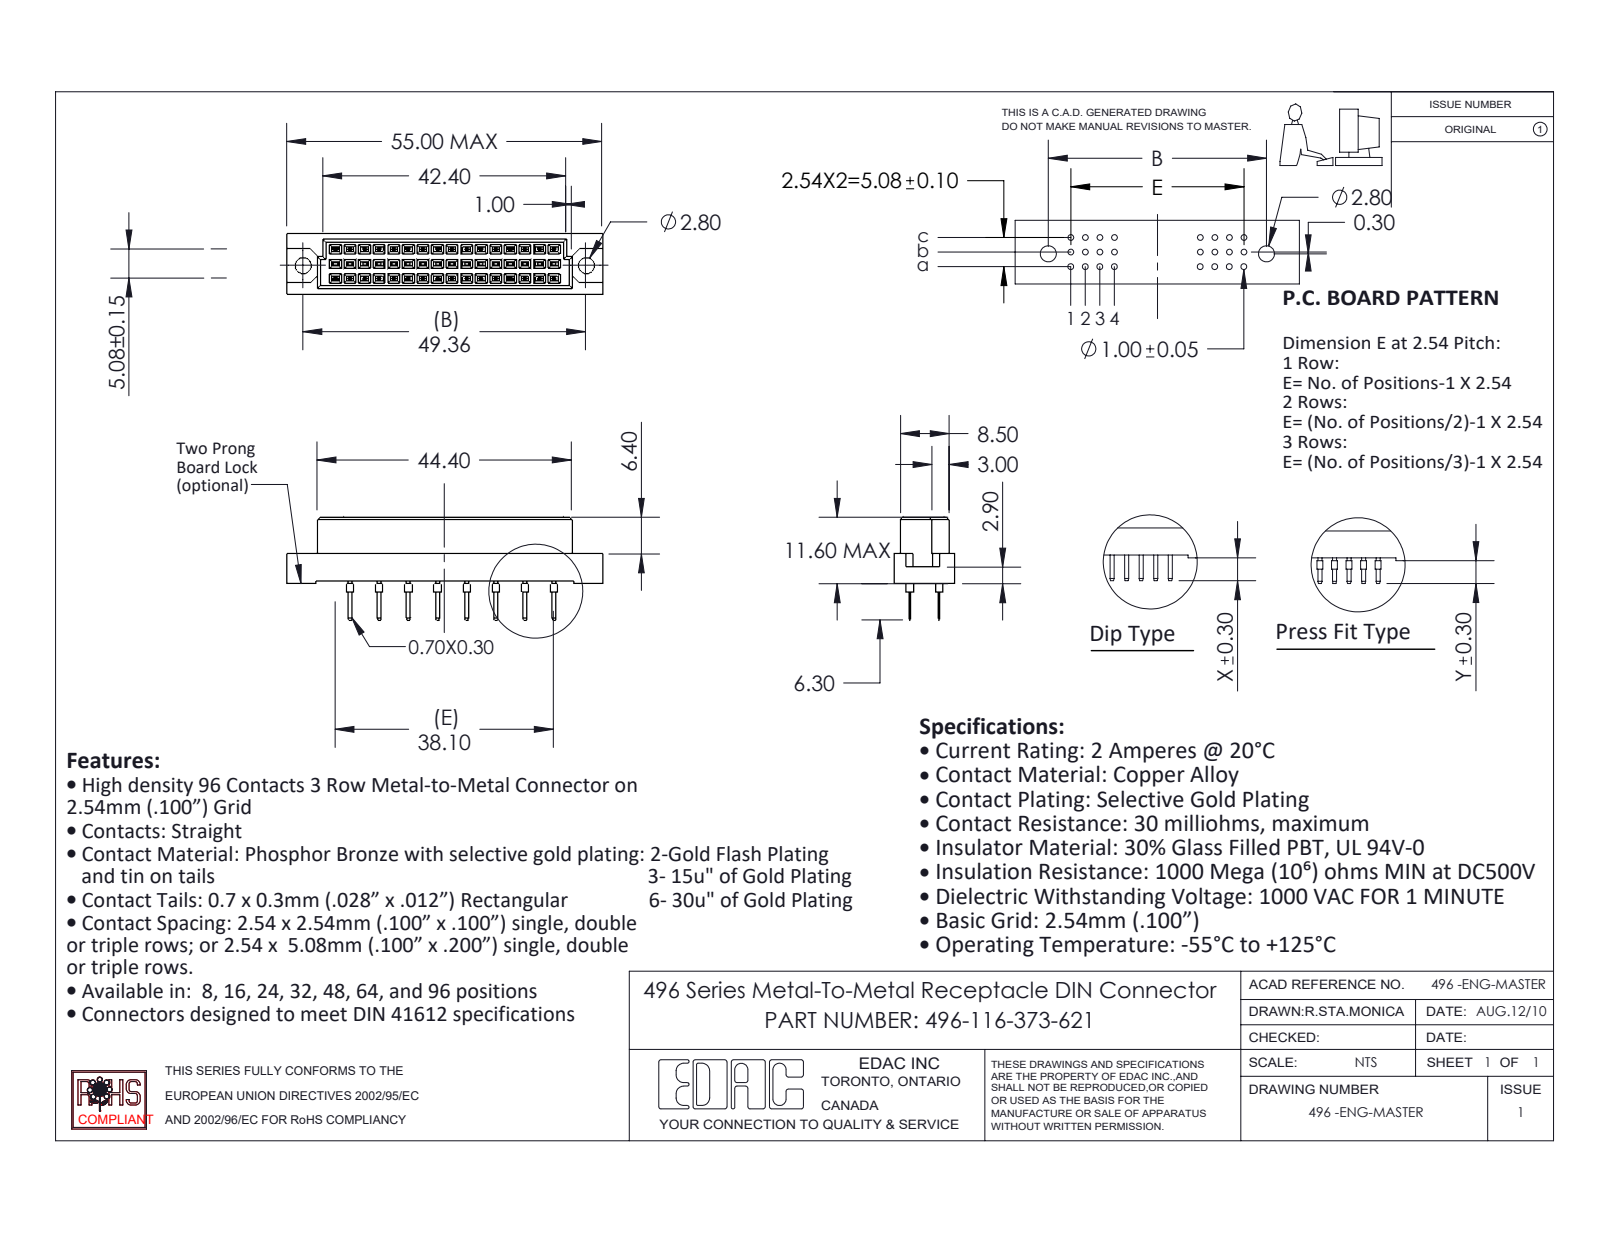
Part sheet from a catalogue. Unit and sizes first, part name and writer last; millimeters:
Units: millimetres
Overall size (bounding box): 55 × 17.9 × 10.6
Round holes (diameter × count): ⌀2.8 ×2
Round bosses / shafts (diameter × count): ⌀1 ×16
Main face-to-face distances: 2.54, 5.08, 1.05, 9.55, 0.81, 0.56, 10.6, 0.55, 3.35, 1.73
Hole centre spacings: 49.36
Volume: 4 639 mm³ · Surface area: 4 607 mm²
Bodies: 17 solids, 954 faces (918 planar, 36 cylindrical, 0 other)
Part name (STEP PRODUCT): 496 Part_48; 496-290_73; 496-116-373-621
STEP written by: SolidWorks 2020 (CONFIG_CONTROL_DESIGN)
